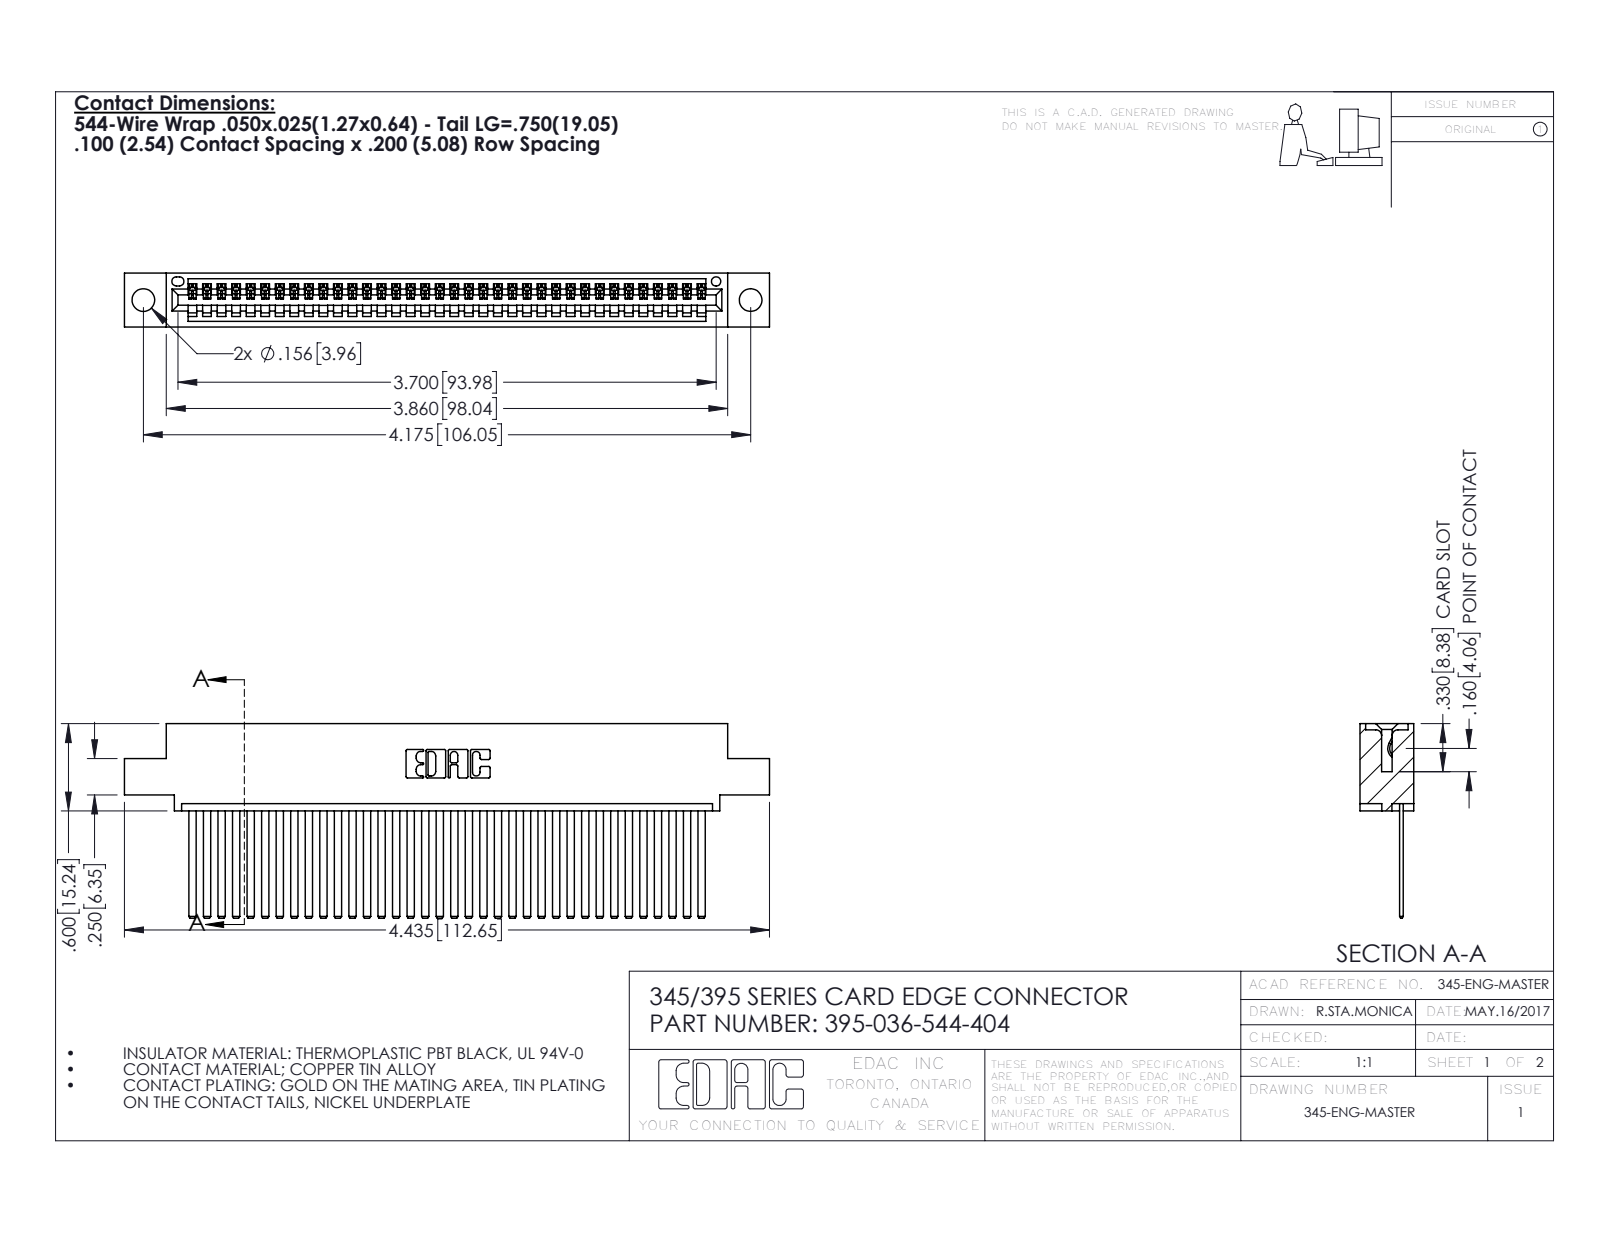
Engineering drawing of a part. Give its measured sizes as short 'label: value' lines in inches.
name: 345 Part_0.110 Offset - 0.156 Dia-TH; 345-292-001_345-293-144; 395-036-544-404
written by: SolidWorks 2016 (CONFIG_CONTROL_DESIGN)
unit: in
bodies: 37 solids, 2002 faces (1380 planar, 622 cylindrical, 0 other)
size: 4.435 × 1.337 × 0.37
volume: 0.666 in³; area: 24.11 in²
holes: 2× ⌀0.156, 1× ⌀0.064
rounds: 72× R0.006, 22× R0.01, 6× R0.007, 6× R0.031, 3× R0.026, 2× R0.031, 2× R0.04, 1× R0.014
face distances: 0.072, 0.298, 0.025, 0.098, 0.272, 0.37, 0.2, 0.225, 0.149, 0.072
hole spacings: 0.27, 3.939, 4.175
